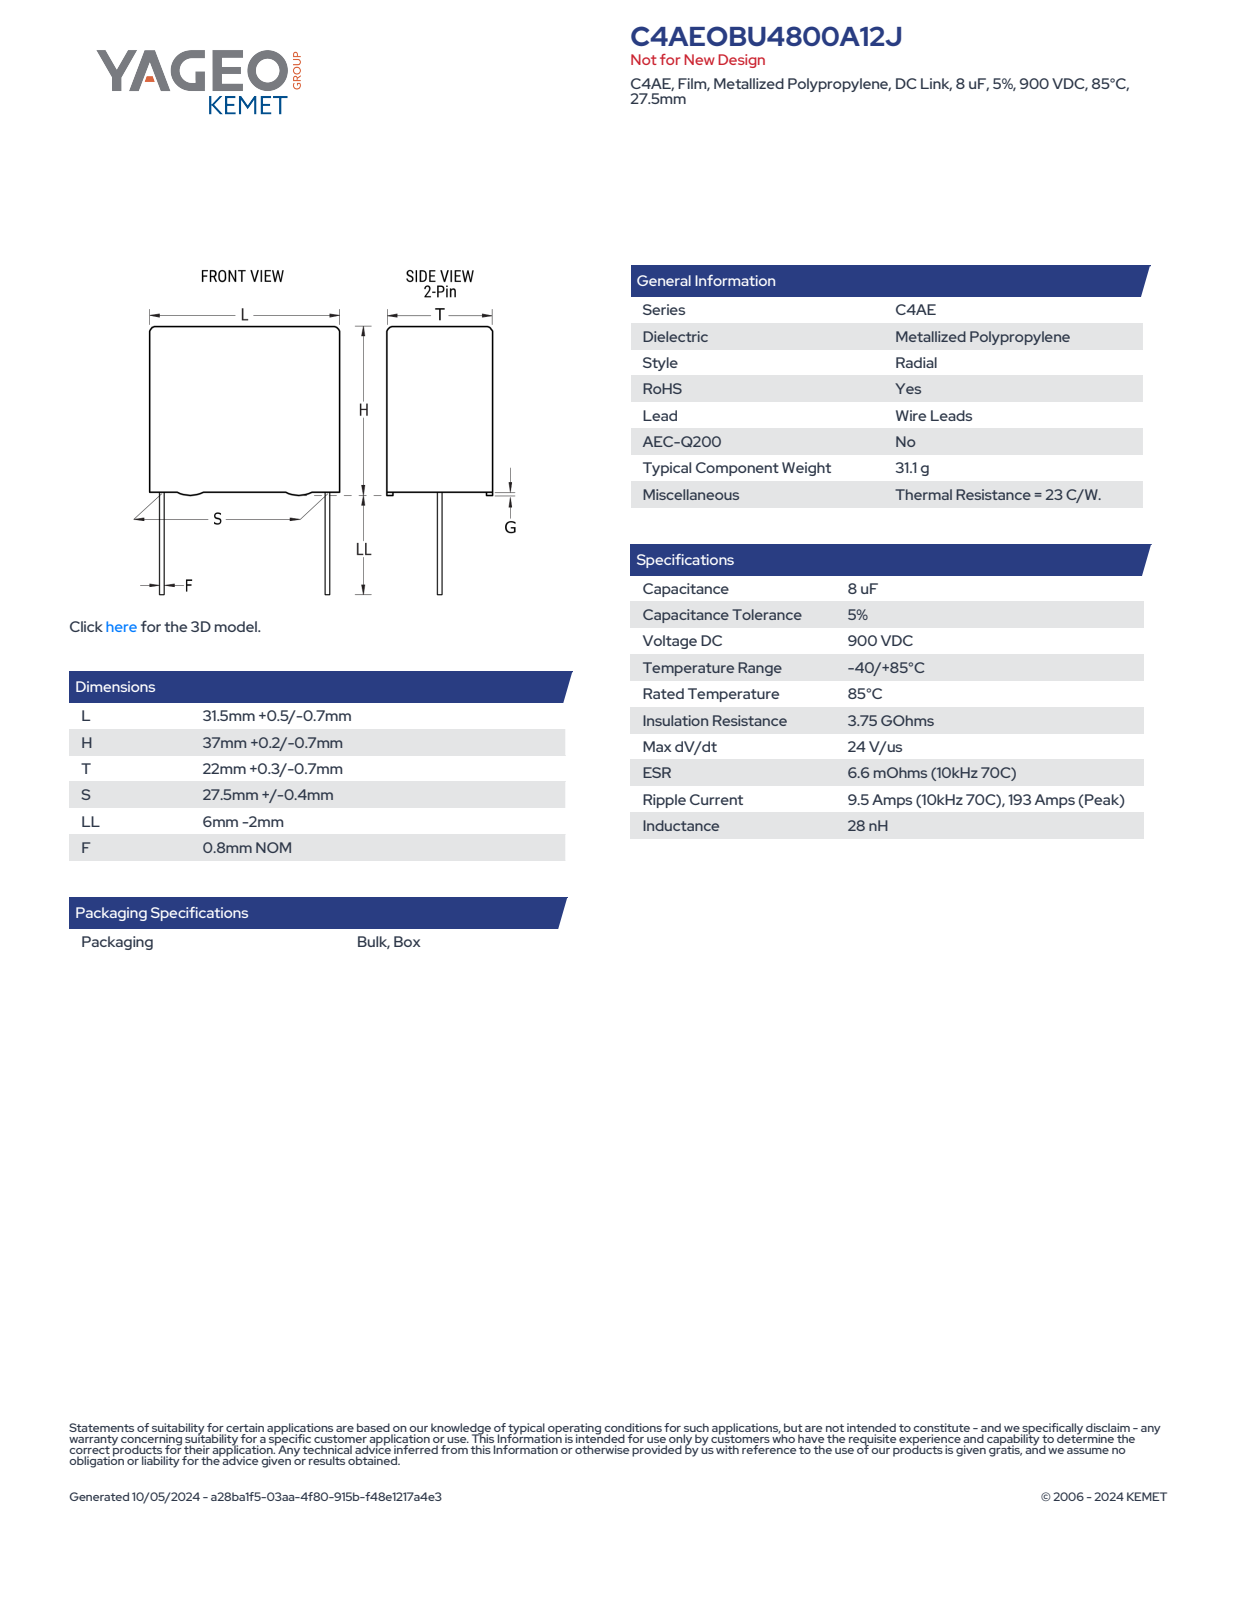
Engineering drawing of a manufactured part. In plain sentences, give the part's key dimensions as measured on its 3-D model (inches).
The part is named "CFP_RBG_31.5X37X22_L32H37.2T22.3S27.9LL4F0.8G0.5". Its 3-D file was written by "SolidWorks 2014 (AUTOMOTIVE_DESIGN)". It is 4 solids with 89 faces: 81 planar, 8 cylindrical and 0 other. Overall it measures 1.622 by 1.26 by 0.878 inches. Its volume is 1.599 cubic inches and its surface area 8.581 square inches. Round bosses or shafts: 2 of diameter 0.031. Partial cylindrical surfaces (rounded edges, fillets, slot ends): 4 of radius 0.02. The main face-to-face distances are 0.878, 1.26, 1.445, 0.02, 1.465, 0.8, 0.078, 0.723, 0.739, 0.157.
